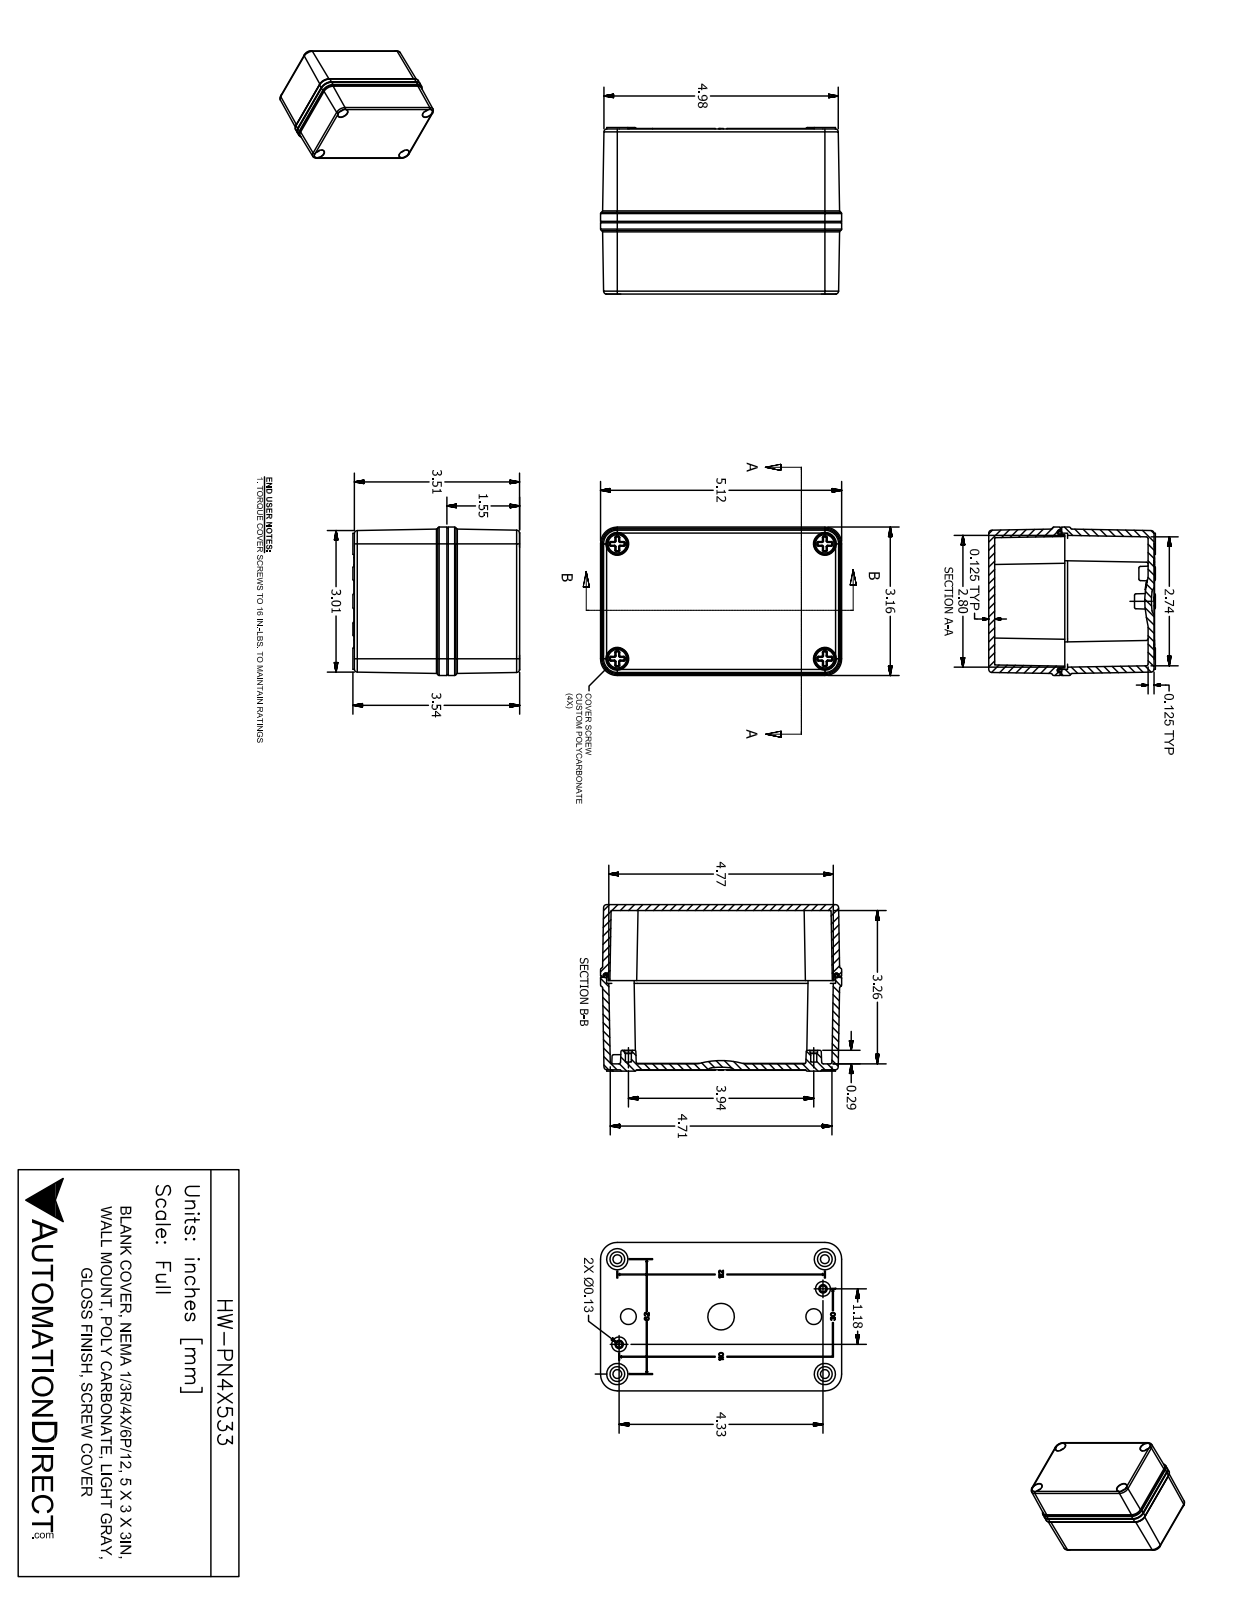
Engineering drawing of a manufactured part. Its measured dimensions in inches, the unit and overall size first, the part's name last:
Units: inches
Overall size (bounding box): 5.124 × 3.54 × 3.156
Round holes (diameter × count): ⌀0.1 ×6, ⌀0.187 ×4, ⌀0.393 ×4, ⌀0.46 ×4
Round bosses / shafts (diameter × count): ⌀0.5 ×4, ⌀0.433 ×4, ⌀0.276 ×4, ⌀0.1 ×2
Partial cylindrical surfaces — rounded edges, fillets, slot ends (radius × count): R0.02 ×48, R0.01 ×32, R0.015 ×14, R0.018 ×8, R0.019 ×8, R0.03 ×8, R0.04 ×8, R0.063 ×8
Main face-to-face distances: 0.135, 0.161, 3.51, 3.375, 3.385, 3.25, 0.125, 1.965, 1.83, 1.42
Hole centre spacings: 2.44, 2.441, 4.409, 4.409, 0.57, 4.333, 5.039, 5.04
Volume: 13.55 in³ · Surface area: 199.8 in²
Bodies: 7 solids, 1020 faces (212 planar, 364 cylindrical, 444 other)
Part name (STEP PRODUCT): HW-PN4X533
STEP written by: SolidWorks 2017 (AUTOMOTIVE_DESIGN)
